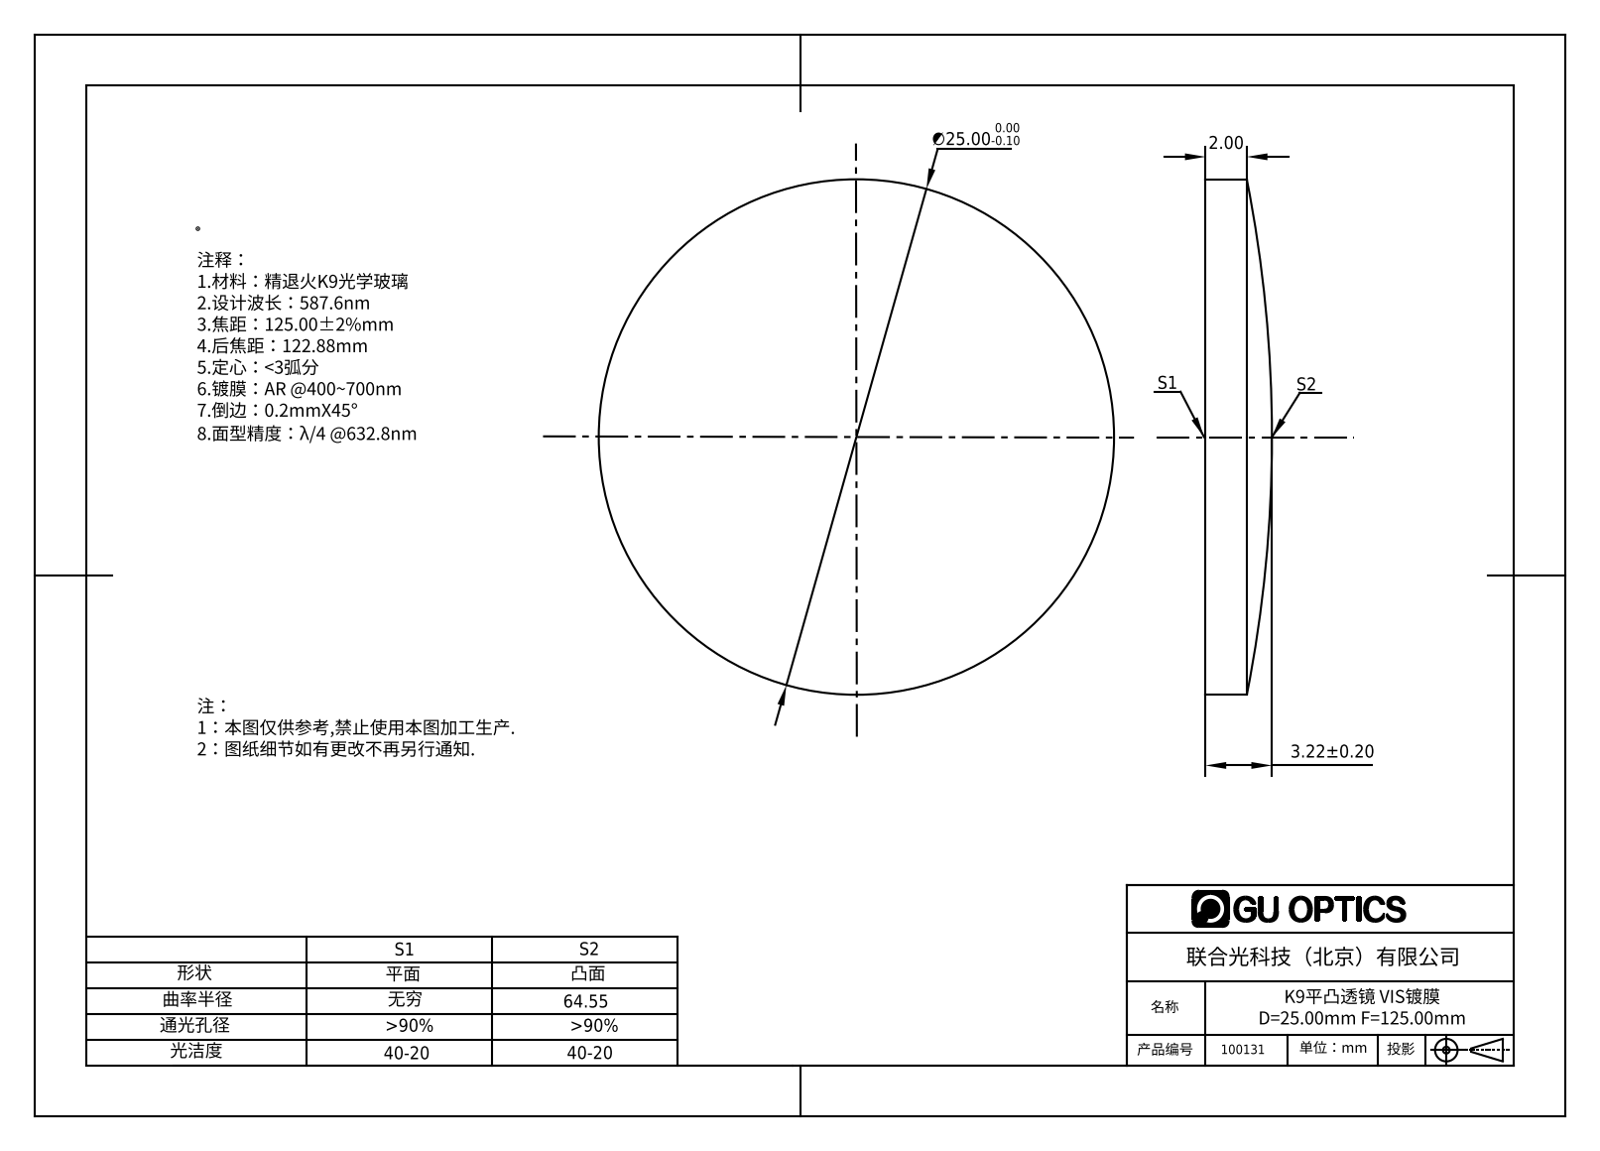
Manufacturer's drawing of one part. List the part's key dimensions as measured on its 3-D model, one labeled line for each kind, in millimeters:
Part name (STEP PRODUCT): 100131
STEP written by: SolidWorks 2016 (AUTOMOTIVE_DESIGN)
Units: millimetres
Bodies: 1 solid, 5 faces (1 planar, 2 cylindrical, 2 other)
Overall size (bounding box): 25 × 25 × 3.22
Volume: 1 282 mm³ · Surface area: 1 144 mm²
Round bosses / shafts (diameter × count): ⌀25 ×1
